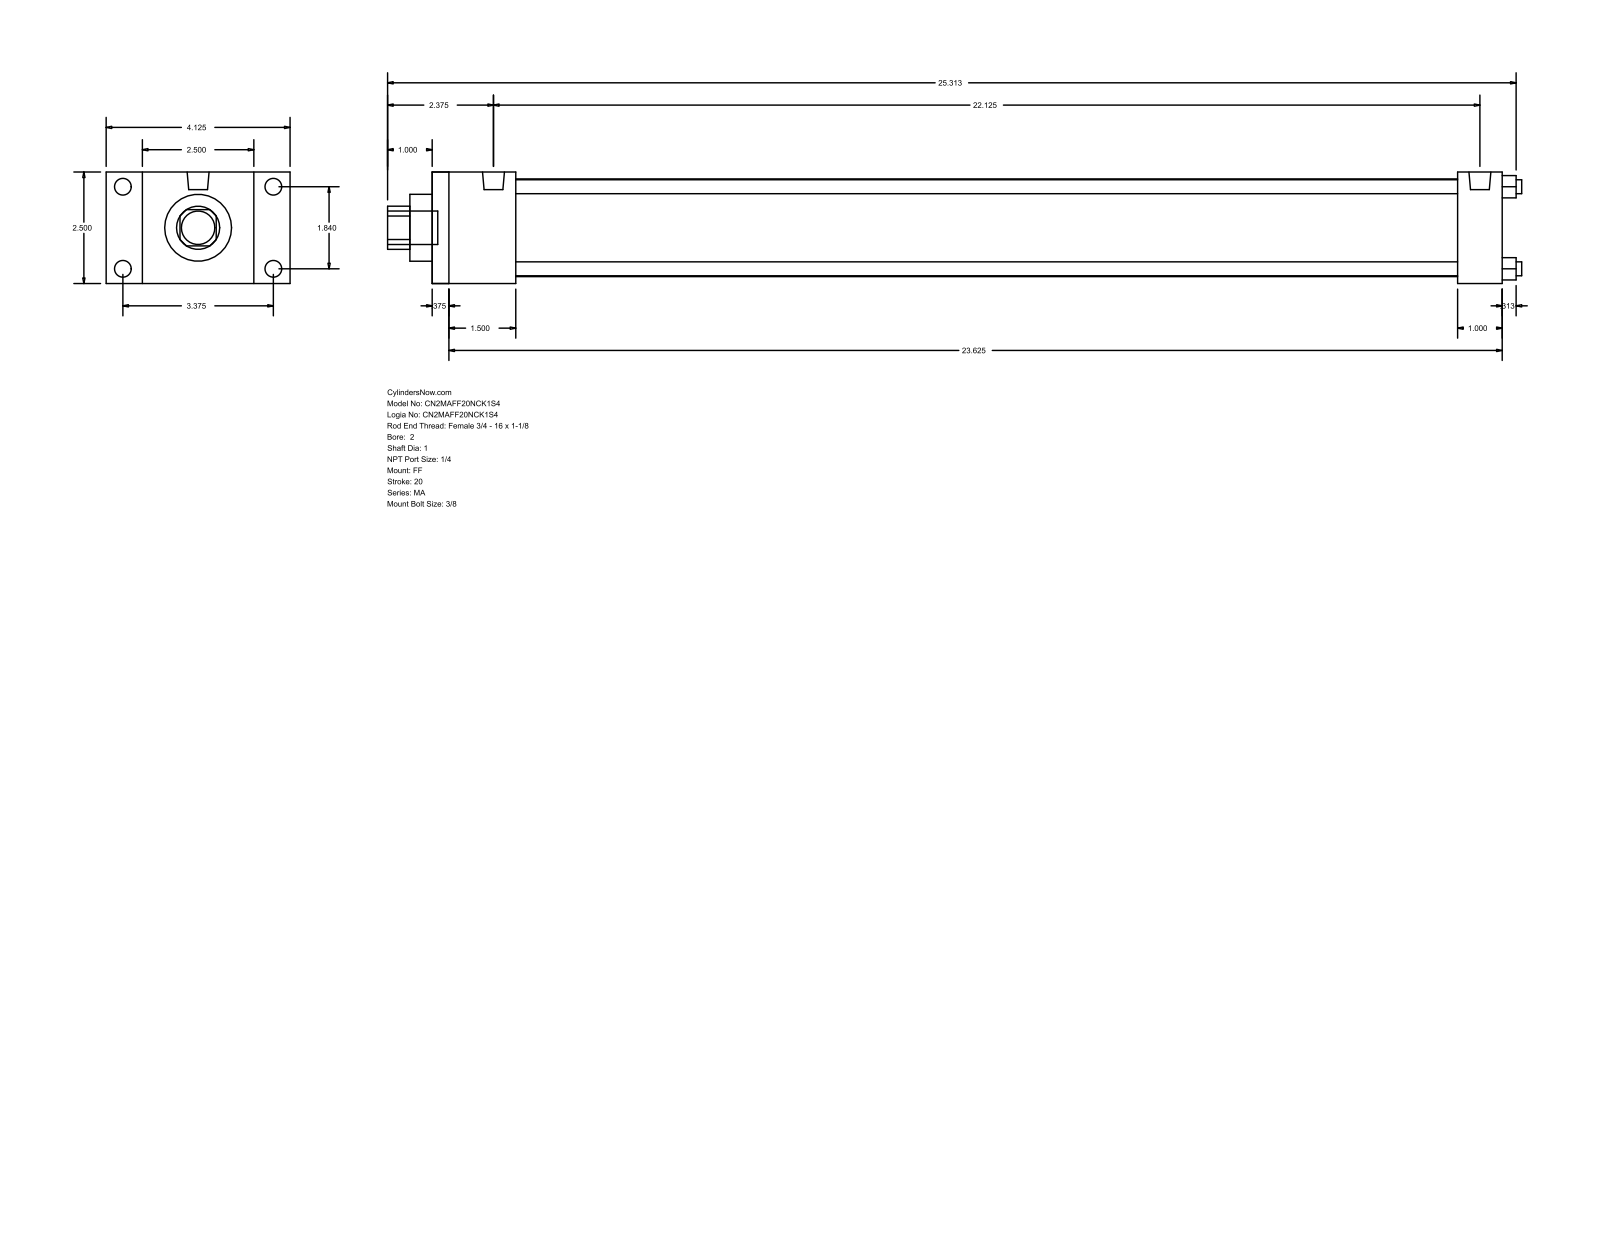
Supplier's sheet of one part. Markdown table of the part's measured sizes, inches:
| quantity | value |
| --- | --- |
| part name | MA_FF__0200_1 |
| STEP written by | GSSL Pune (CONFIG_CONTROL_DESIGN) |
| units | inches |
| bodies | 0 solids, 92 faces (64 planar, 28 cylindrical, 0 other) |
| overall size | 25.437 × 4.125 × 2.5 |
| round holes (diameter × count) | 0.313 × 4, 1 × 1, 1.5 × 1, 2.19 × 1 |
| round bosses / shafts (diameter × count) | 0.375 × 4, 0.313 × 4, 0.492 × 2, 0.75 × 1 |
| partial cylindrical surfaces (radius × count) | 0.484 × 1 |
| main face-to-face distances | 2.5, 24, 0.375, 23.625, 1, 0.813, 0.5, 1.875, 23, 1.5 |
| hole center spacings | 1.301, 1.84, 2.602 |
